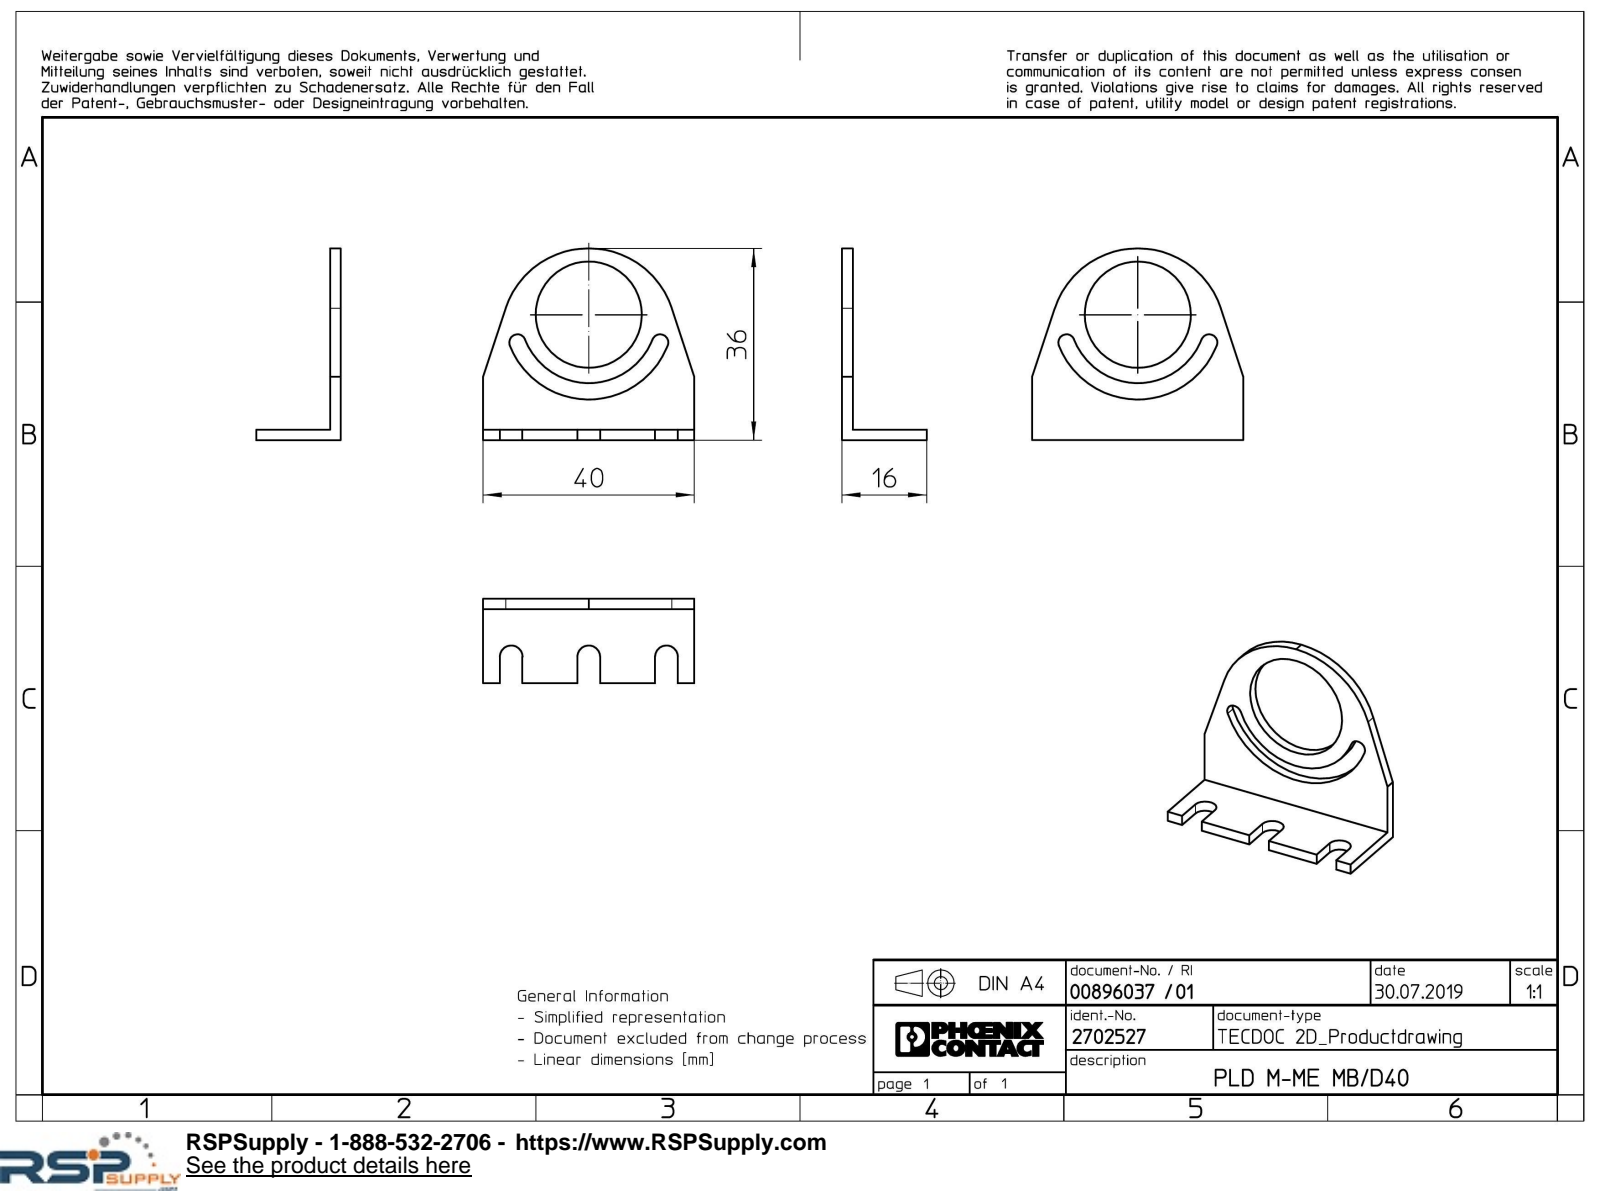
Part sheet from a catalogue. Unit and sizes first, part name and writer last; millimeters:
Units: millimetres
Overall size (bounding box): 40 × 36.25 × 16
Round holes (diameter × count): ⌀20.1 ×1
Partial cylindrical surfaces — rounded edges, fillets, slot ends (radius × count): R2.15 ×3, R1.55 ×2, R16.5 ×2, R12.95 ×1, R16.05 ×1
Main face-to-face distances: 2, 16, 14, 40, 14.7, 4.3, 7.45, 32.55, 17.85, 22.15
Volume: 2 488 mm³ · Surface area: 3 169 mm²
Bodies: 1 solid, 30 faces (19 planar, 11 cylindrical, 0 other)
Part name (STEP PRODUCT): PLD_M_ME_MB_D40-select
STEP written by: Creo Elements/Direct Modeling 20.1A 29-Sep-2018 (C) Parametric Technology GmbH (AUTOMOTIVE_DESIGN)
